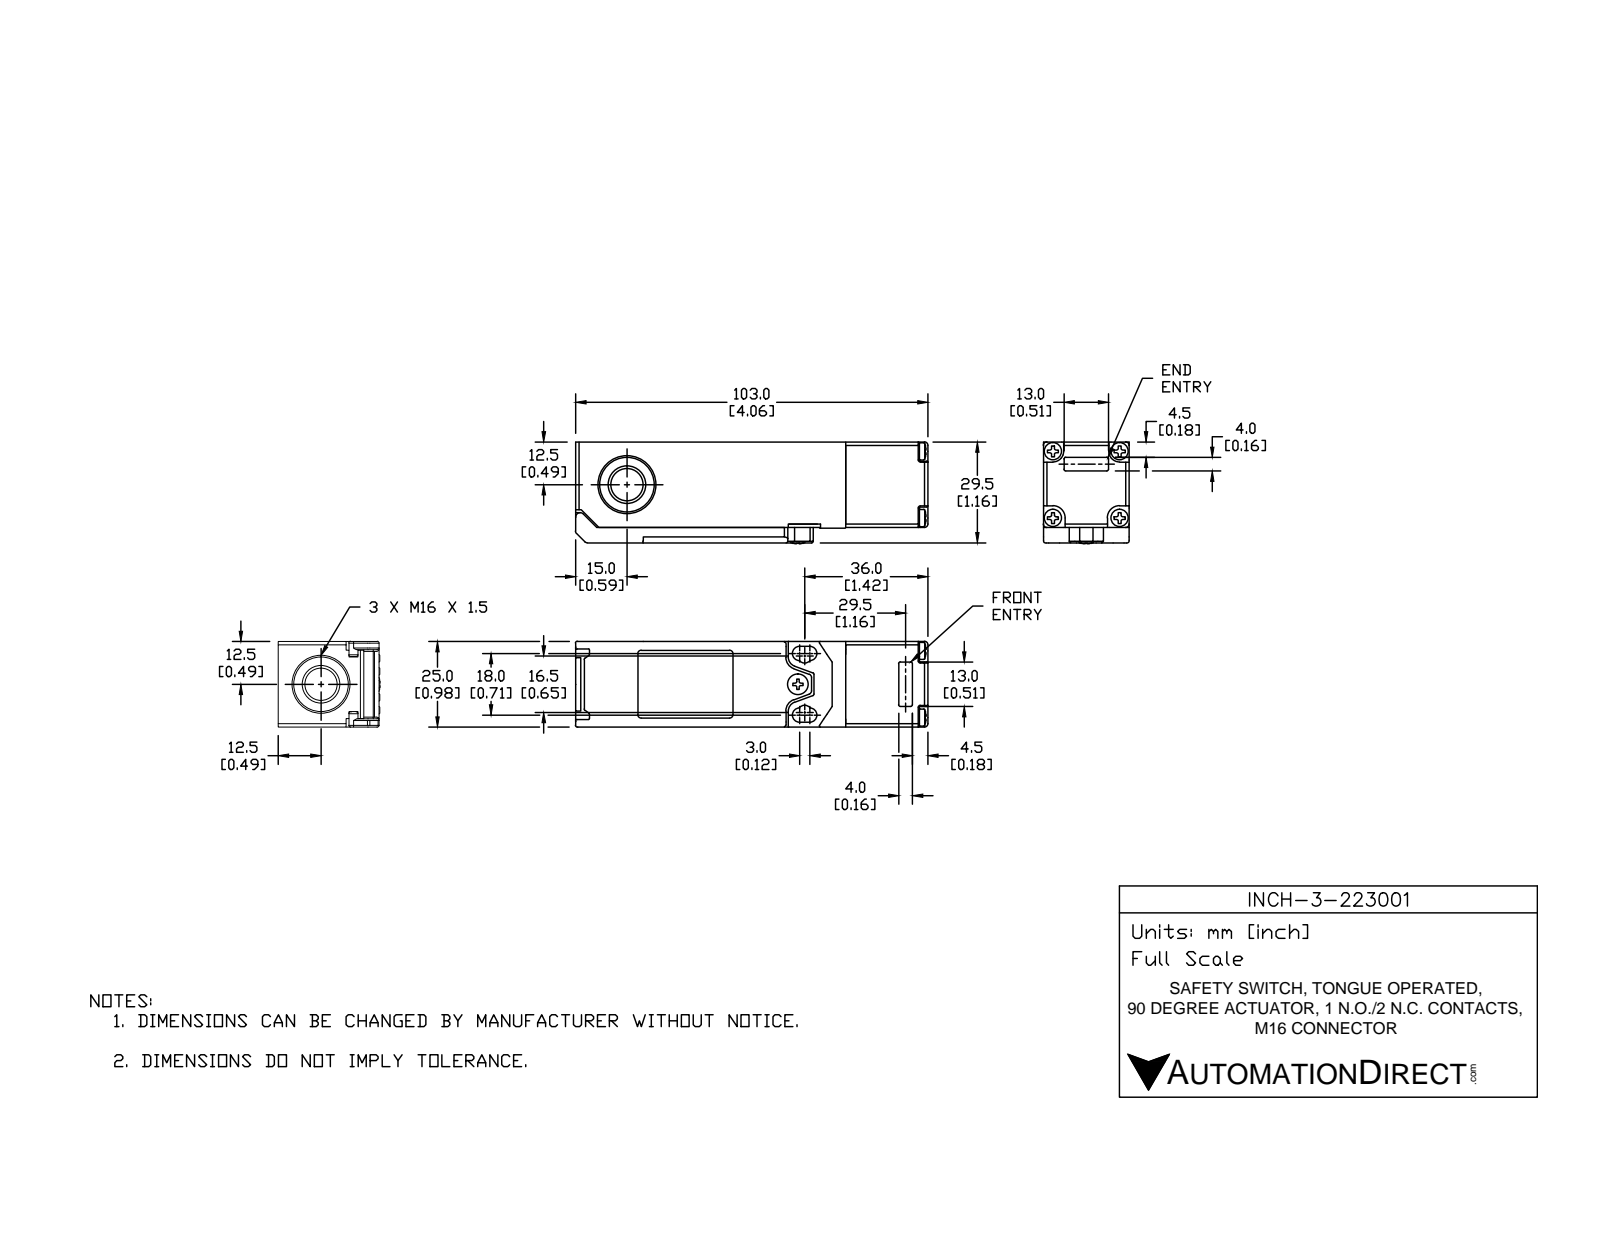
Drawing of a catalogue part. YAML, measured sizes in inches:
part_name: "INCH-3-223001"
step_written_by: "SolidWorks 2014 (AUTOMOTIVE_DESIGN)"
units: inches
bodies: {solids: 12, faces: 1860, planar: 865, cylindrical: 591, other: 404}
overall_size: [4.055, 1.172, 0.984]
volume: 1.717
surface_area: 47.09
round_holes:
  - {diameter: 0.126, count: 5}
  - {diameter: 0.094, count: 4}
  - {diameter: 0.059, count: 2}
  - {diameter: 0.063, count: 2}
  - {diameter: 0.071, count: 2}
  - {diameter: 0.087, count: 2}
  - {diameter: 0.142, count: 2}
  - {diameter: 0.63, count: 2}
  - {diameter: 0.055, count: 1}
  - {diameter: 0.098, count: 1}
  - {diameter: 0.102, count: 1}
  - {diameter: 0.197, count: 1}
round_bosses_or_shafts:
  - {diameter: 0.102, count: 5}
  - {diameter: 0.197, count: 4}
  - {diameter: 0.079, count: 4}
  - {diameter: 0.138, count: 2}
  - {diameter: 0.213, count: 1}
  - {diameter: 0.118, count: 1}
  - {diameter: 0.051, count: 1}
partial_cylinders:
  - {radius: 0.02, count: 209}
  - {radius: 0.012, count: 52}
  - {radius: 0.039, count: 25}
  - {radius: 0.004, count: 24}
  - {radius: 0.031, count: 10}
  - {radius: 0.083, count: 6}
  - {radius: 0.11, count: 6}
  - {radius: 0.008, count: 4}
face_to_face_distances: [0.984, 0.079, 0.098, 0.177, 0.906, 0.039, 0.071, 0.913, 0.051, 0.087]
hole_center_spacings: [0.543, 0.768, 0.171, 0.187, 0.423, 0.426, 0.45, 0.581]
